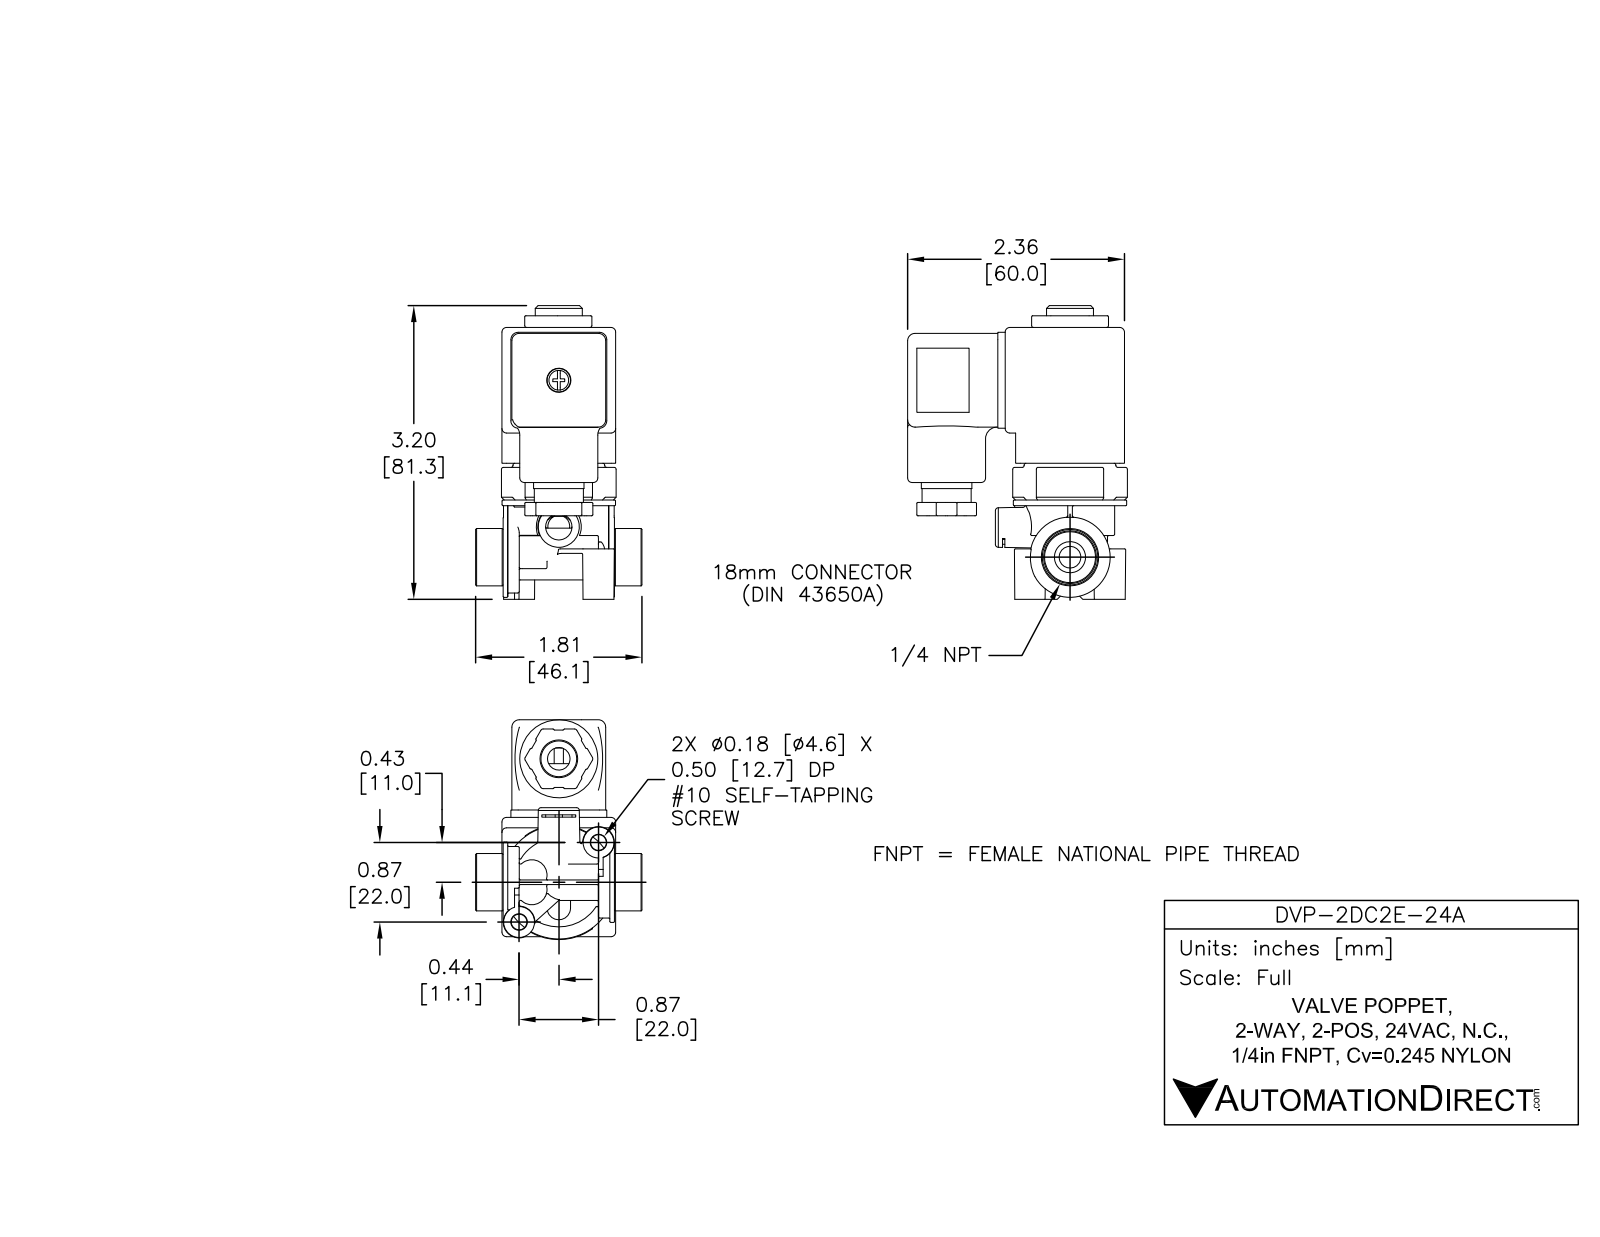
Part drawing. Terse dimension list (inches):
name: DVP-2DC2E-24A
written by: SolidWorks 2015 (AUTOMOTIVE_DESIGN)
unit: in
bodies: 6 solids, 1820 faces (805 planar, 354 cylindrical, 661 other)
size: 3.216 × 2.395 × 1.813
volume: 3.952 in³; area: 54.42 in²
holes: 2× ⌀0.06, 2× ⌀0.236, 1× ⌀0.095, 1× ⌀0.102, 1× ⌀0.12, 1× ⌀0.203, 1× ⌀0.245, 1× ⌀0.25, 1× ⌀0.263, 1× ⌀0.287, 1× ⌀0.37, 1× ⌀0.39
bosses: 2× ⌀0.29, 1× ⌀1.236, 1× ⌀1, 1× ⌀0.972, 1× ⌀0.922, 1× ⌀0.89, 1× ⌀0.875, 1× ⌀0.85
rounds: 75× R0.01, 38× R0.015, 21× R0.05, 12× R0.02, 12× R0.08, 6× R0.026, 6× R0.03, 4× R0.04
face distances: 1.083, 1.24, 0.048, 0.157, 0.925, 1.48, 0.109, 1.131, 0.974, 1.367
hole spacings: 0.281, 0.283, 1.062, 1.343, 1.345, 1.612, 1.626, 2.184
